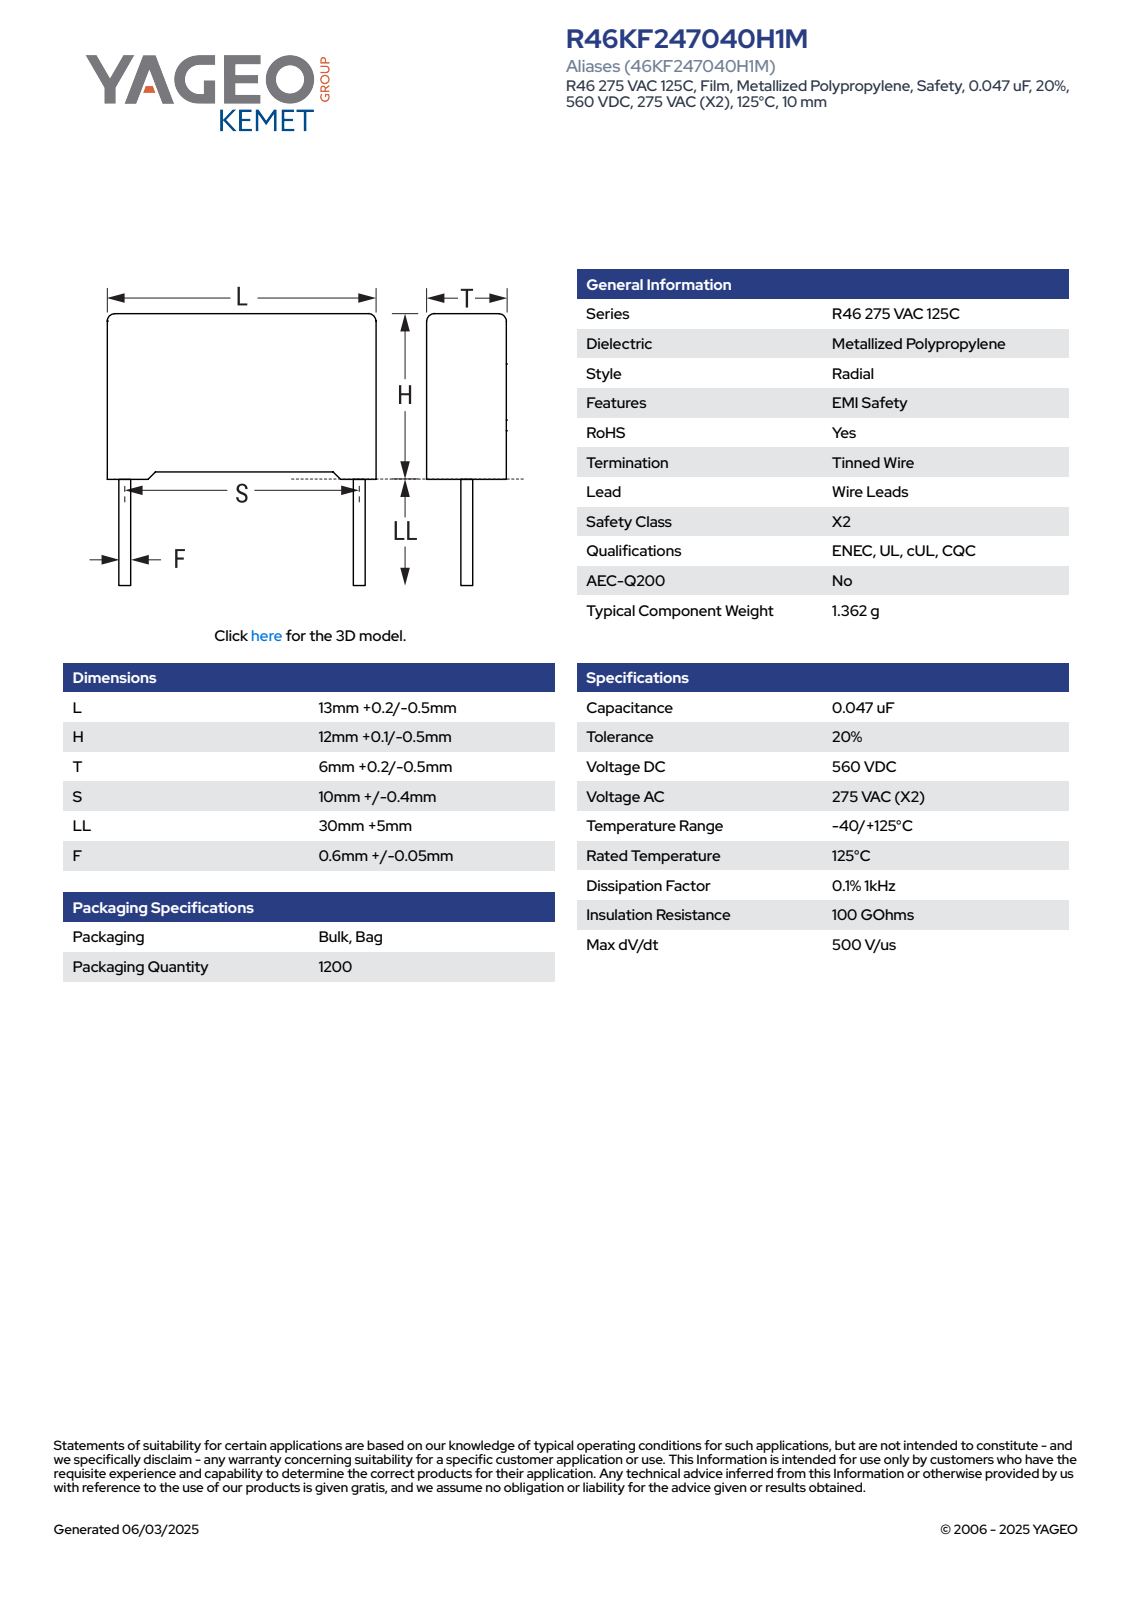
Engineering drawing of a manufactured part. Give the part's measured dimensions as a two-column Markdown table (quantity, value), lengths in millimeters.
| quantity | value |
| --- | --- |
| part name | CFR_RB2_13X12X6_L13.2H12.1T6.2S10LL35F0.65 |
| STEP written by | SolidWorks 2021 (AUTOMOTIVE_DESIGN) |
| units | millimeters |
| bodies | 4 solids, 85 faces (77 planar, 8 cylindrical, 0 other) |
| overall size | 47.1 × 13.2 × 6.21 |
| volume | 960 mm³ |
| surface area | 800 mm² |
| round bosses / shafts (diameter × count) | 0.65 × 2 |
| partial cylindrical surfaces (radius × count) | 0.5 × 4 |
| main face-to-face distances | 6.2, 13.2, 11.35, 0.44, 5.76, 0.75, 12.1, 12.76, 5.32, 0.42 |
